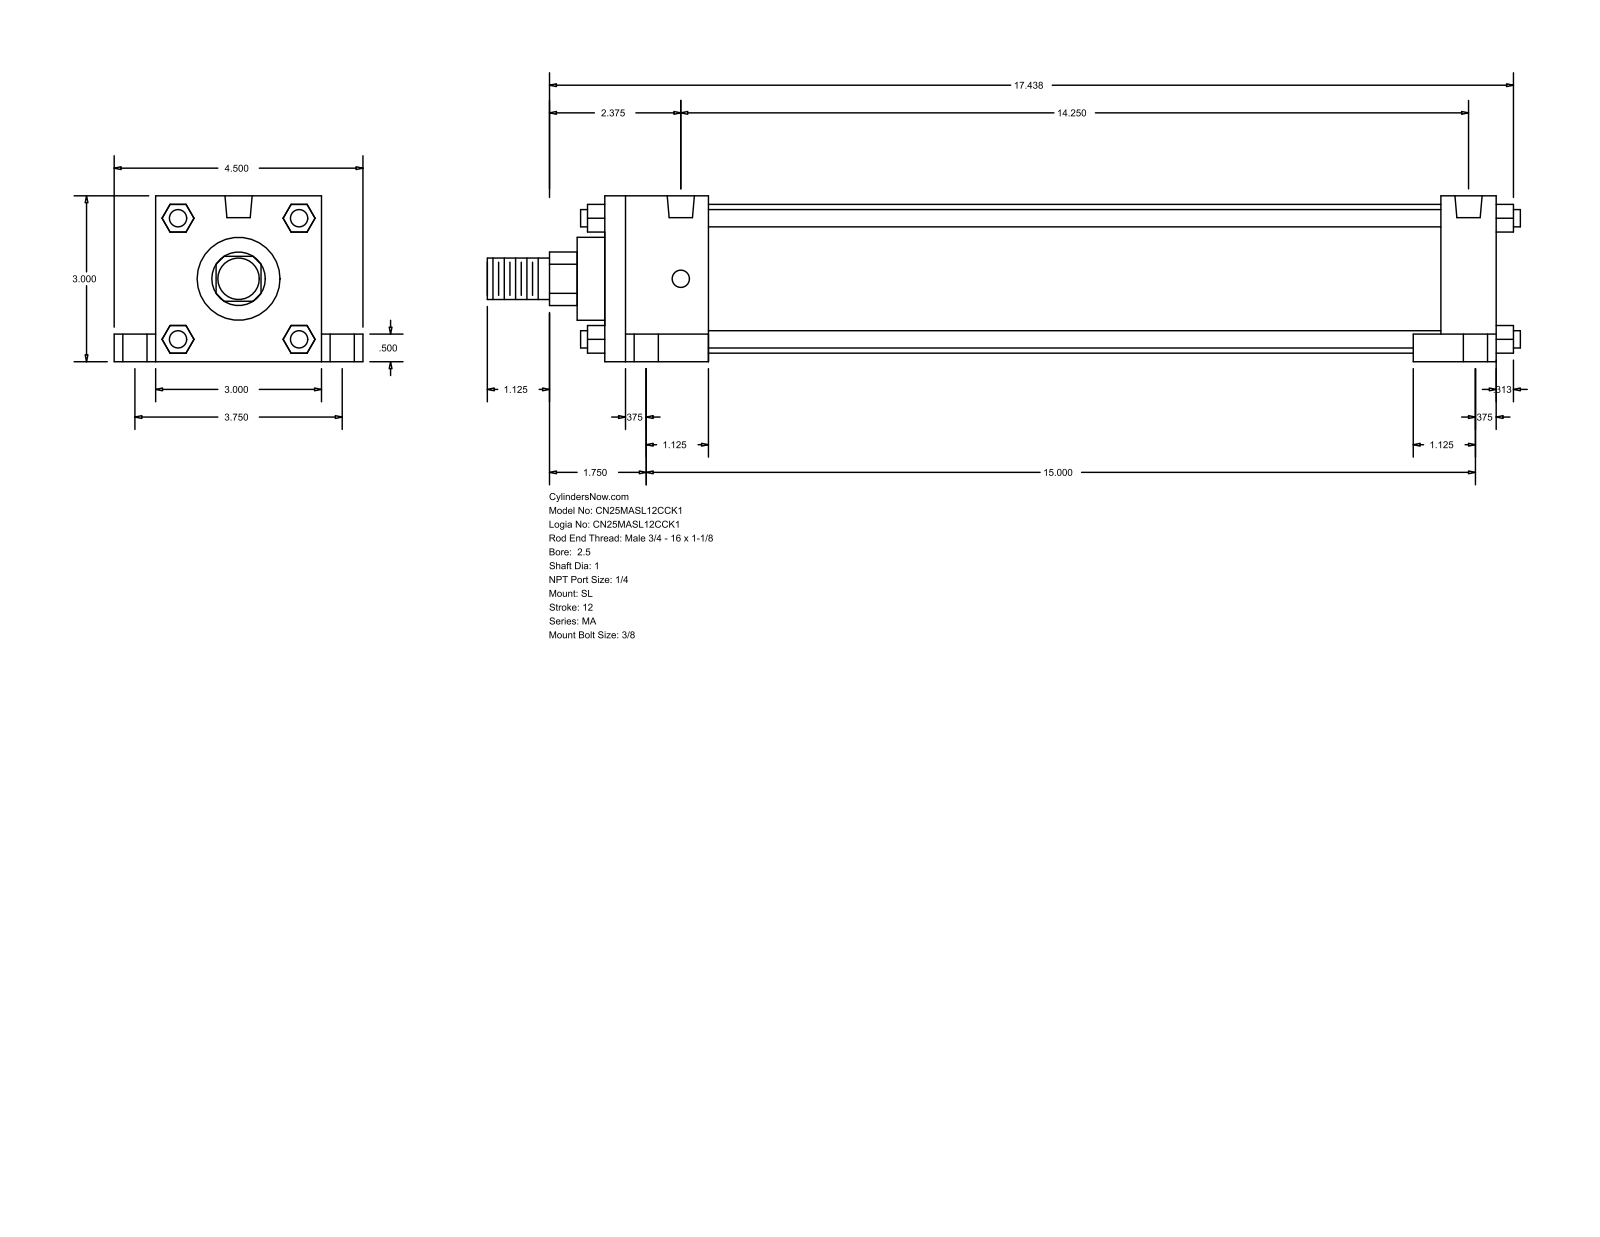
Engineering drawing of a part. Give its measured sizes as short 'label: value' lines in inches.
name: MA_SL__0250_1
written by: GSSL Pune (CONFIG_CONTROL_DESIGN)
unit: in
bodies: 0 solids, 148 faces (112 planar, 36 cylindrical, 0 other)
size: 18.687 × 4.5 × 3
holes: 4× ⌀0.313, 4× ⌀0.437, 4× ⌀0.687, 2× ⌀0.492
bosses: 4× ⌀0.313, 1× ⌀2.69, 1× ⌀1.5, 1× ⌀1, 1× ⌀0.75
rounds: 1× R0.484
face distances: 3, 16.125, 0.5, 1.875, 14.25, 15.125, 13.25, 1, 0.75, 3.75
hole spacings: 1.879, 1.976, 3.75, 14.25, 14.496, 14.993, 15, 15.461
